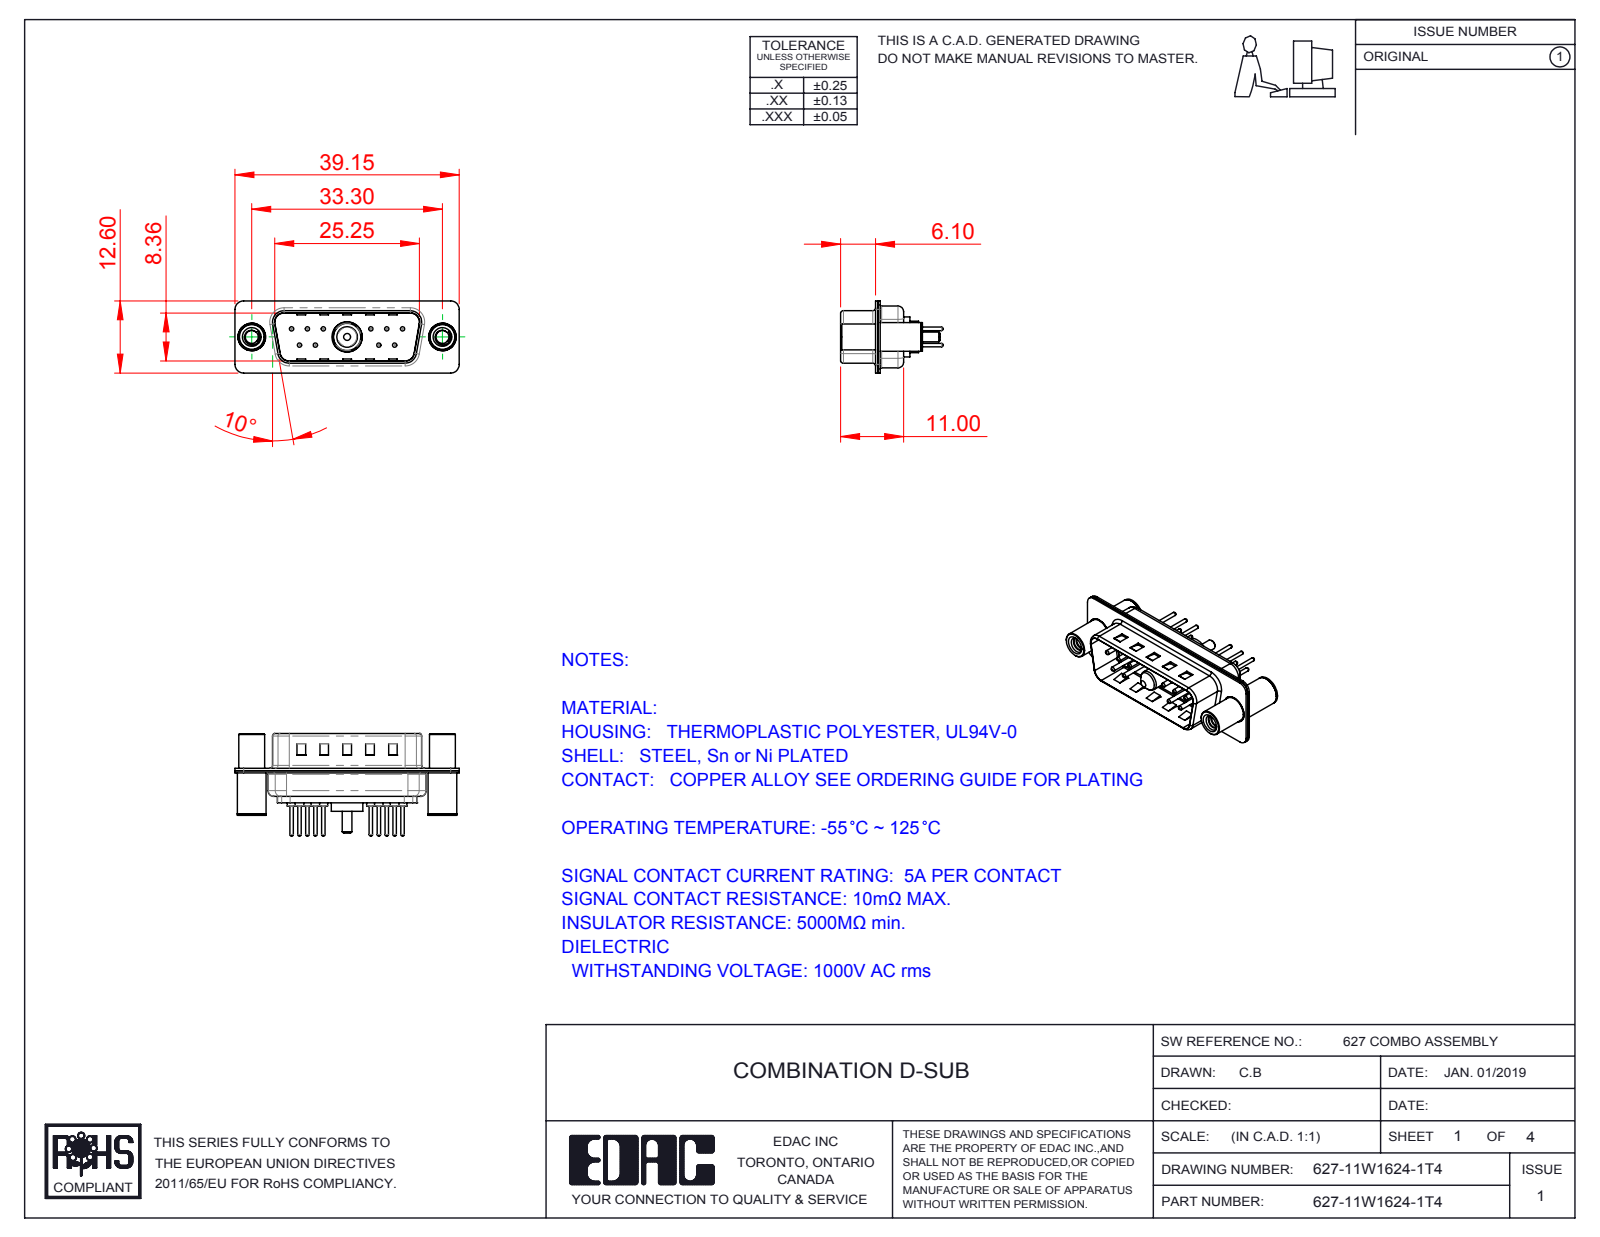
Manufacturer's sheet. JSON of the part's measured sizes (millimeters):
{"part_name": "627Combo Contact Row 2_24; 627Combo Threaded Standoff and Board Spacer_4; 627Combo Shell Rear_15 Contacts; Power Pin_10A S (+4 more)", "step_written_by": "SolidWorks 2016 (CONFIG_CONTROL_DESIGN)", "units": "millimeters", "bodies": {"solids": 17, "faces": 849, "planar": 234, "cylindrical": 348, "other": 267}, "overall_size": [39.15, 17.9, 12.6], "volume_mm3": 2184, "surface_area_mm2": 5306, "round_holes": [[0.75, 10], [1.6, 10], [2, 10], [2.26, 2], [3.26, 2], [4, 2], [4.8, 2], [4.85, 1], [5.3, 1]], "round_bosses_or_shafts": [[1.5, 10], [0.6, 10], [5, 2], [4.9, 2], [4.5, 2], [5.5, 1], [5.2, 1], [4.75, 1]], "partial_cylinders_radius": [[1.5, 20], [2, 12], [0.5, 8], [1.6, 8], [1, 7], [0.25, 4], [0.6, 4], [0.65, 4]], "face_to_face_distances": [0.4, 0.82, 9.58, 8.76, 0.8, 1.5, 5.6, 6, 5.2, 1.22], "hole_center_spacings": [3.16, 2.77, 13.85, 11.08, 16.62, 5.03, 5.04, 5.54]}
